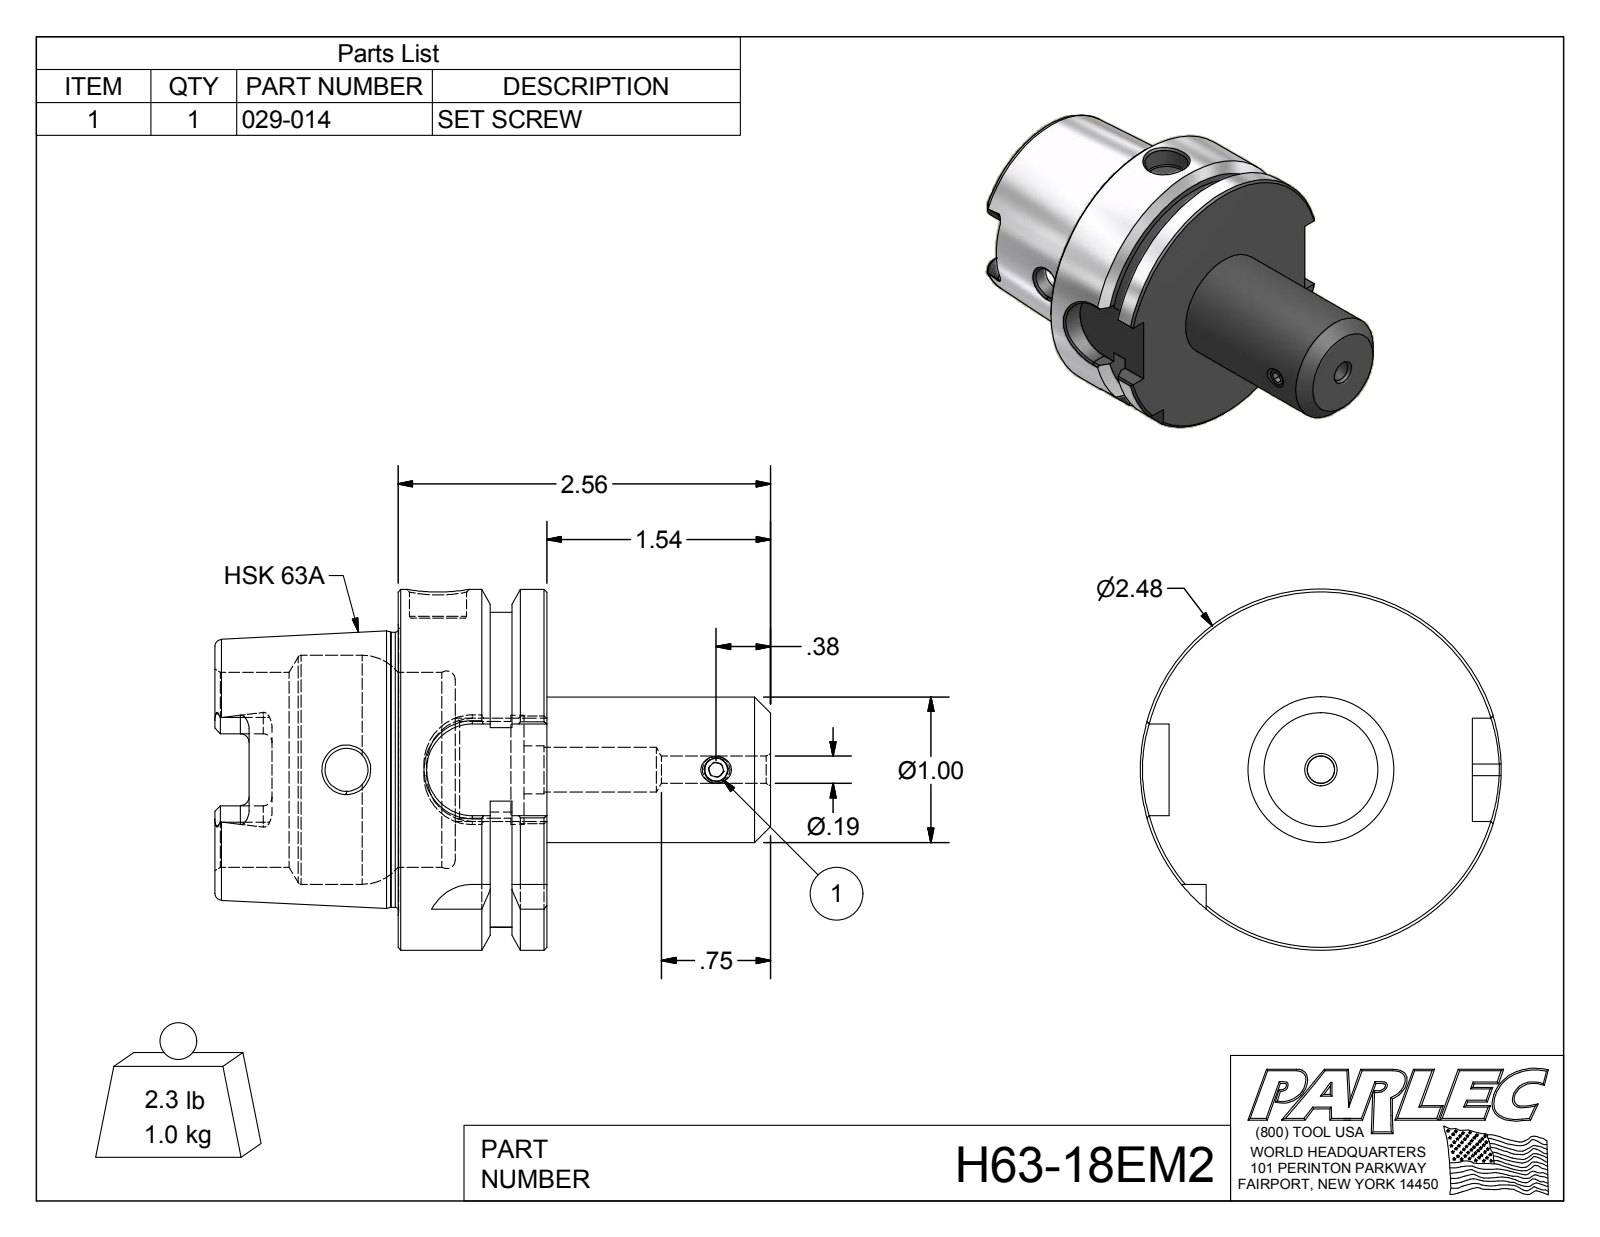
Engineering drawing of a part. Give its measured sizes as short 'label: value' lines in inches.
name: H63-18EM2; H63-18EM2-1; 029-014
written by: Autodesk Inventor 2012 (AUTOMOTIVE_DESIGN)
unit: in
bodies: 2 solids, 149 faces (62 planar, 37 cylindrical, 50 other)
size: 3.822 × 2.48 × 2.48
volume: 6.057 in³; area: 41.17 in²
holes: 1× ⌀0.156, 1× ⌀0.187, 1× ⌀0.295, 1× ⌀0.307, 1× ⌀0.331, 1× ⌀0.394, 1× ⌀0.666, 1× ⌀0.749, 1× ⌀1.339, 1× ⌀1.575
bosses: 1× ⌀2.48, 1× ⌀1.891, 1× ⌀1, 1× ⌀0.19
rounds: 6× R0.059, 4× R0.113, 4× R0.315, 1× R1.083
face distances: 1.024, 0.241, 0.389, 0.394, 0.63, 1.26, 1.654, 2.283, 2.043, 0.783
hole spacings: 2.541
